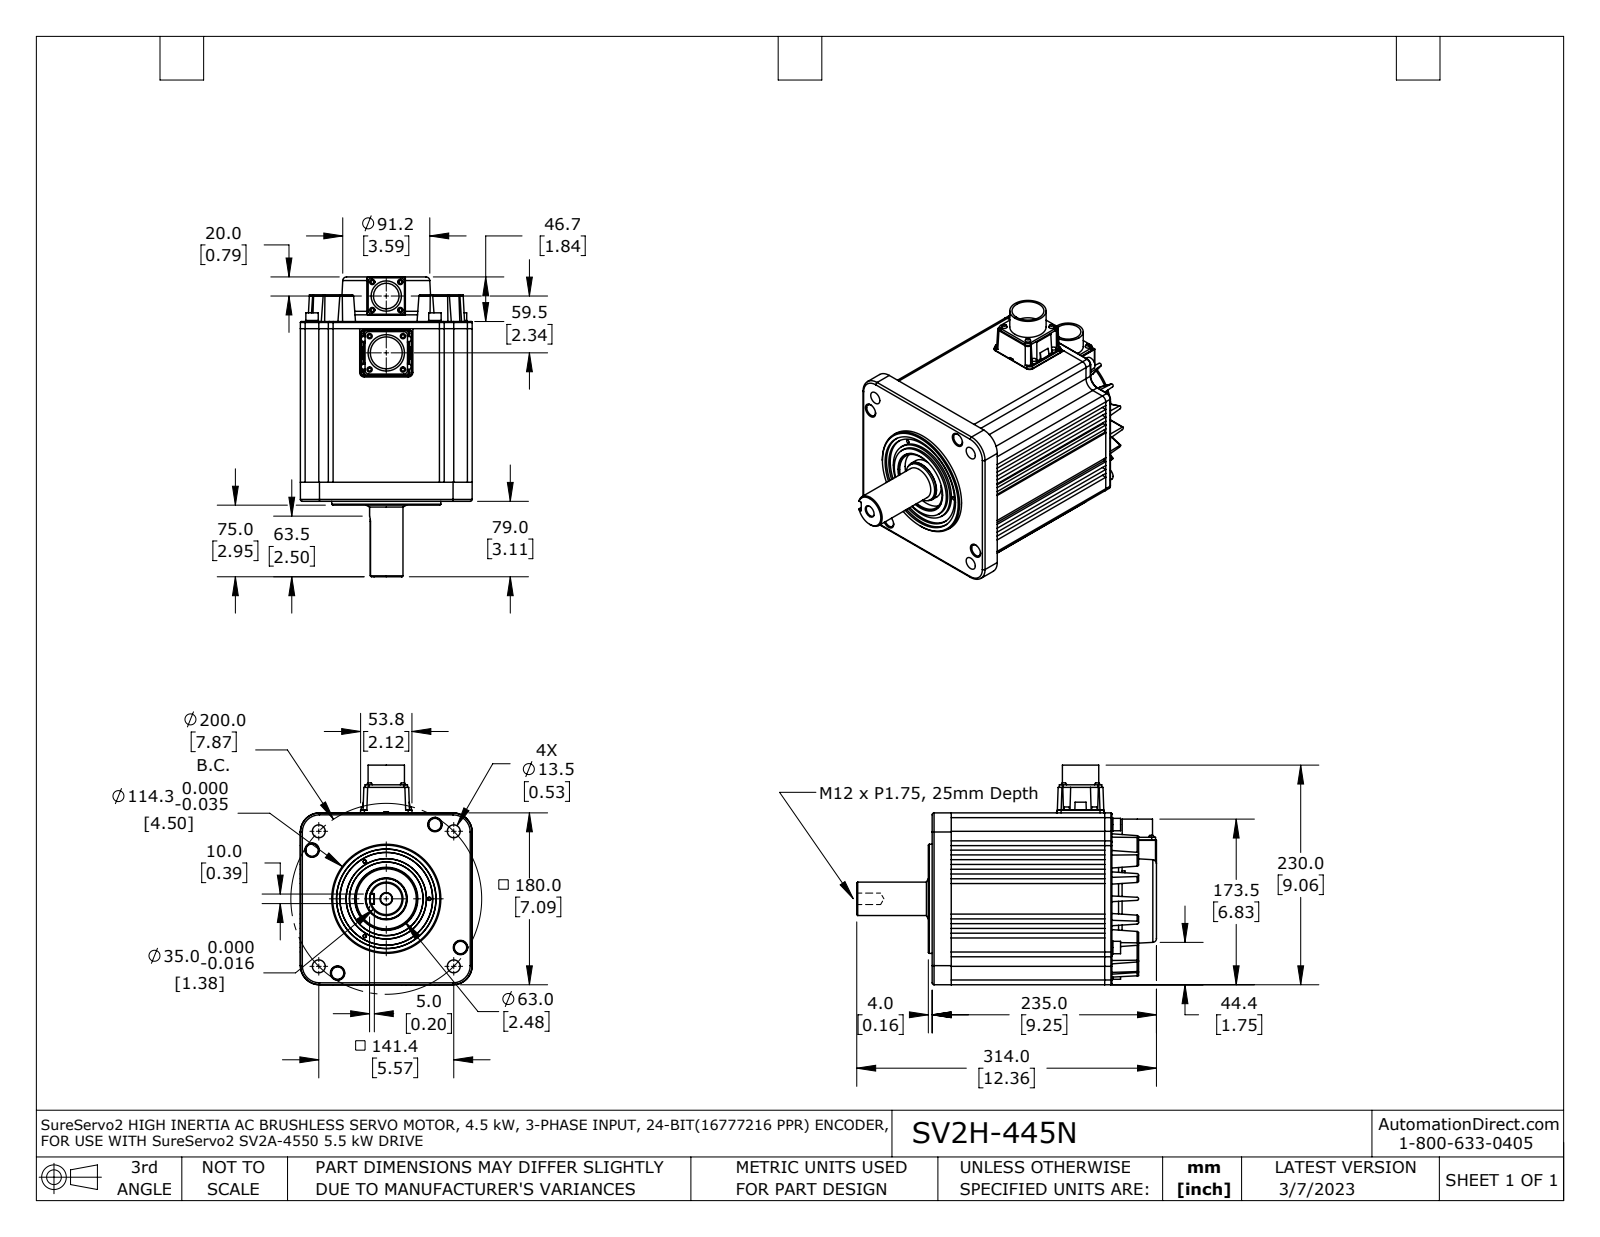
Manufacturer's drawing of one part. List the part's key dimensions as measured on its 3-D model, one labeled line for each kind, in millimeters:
Part name (STEP PRODUCT): SV2H-x45N
STEP written by: SolidWorks 2021 (AUTOMOTIVE_DESIGN)
Units: millimetres
Bodies: 1 solid, 627 faces (319 planar, 202 cylindrical, 106 other)
Overall size (bounding box): 314 × 230 × 180
Volume: 5 993 000 mm³ · Surface area: 315 500 mm²
Round holes (diameter × count): ⌀13.5 ×4, ⌀12 ×1, ⌀26.9 ×1, ⌀33.5 ×1, ⌀63 ×1
Round bosses / shafts (diameter × count): ⌀5.5 ×7, ⌀13.4 ×4, ⌀13 ×4, ⌀8 ×4, ⌀116 ×1, ⌀114.3 ×1, ⌀44 ×1, ⌀42.5 ×1
Partial cylindrical surfaces — rounded edges, fillets, slot ends (radius × count): R5 ×17, R1.6 ×16, R4 ×16, R1 ×12, R0.5 ×8, R2 ×4, R10 ×4, R20 ×4
Main face-to-face distances: 5, 180, 10, 29.3, 150.7, 15, 77, 188.3, 82, 72
Hole centre spacings: 100, 141.4, 200, 59.5
